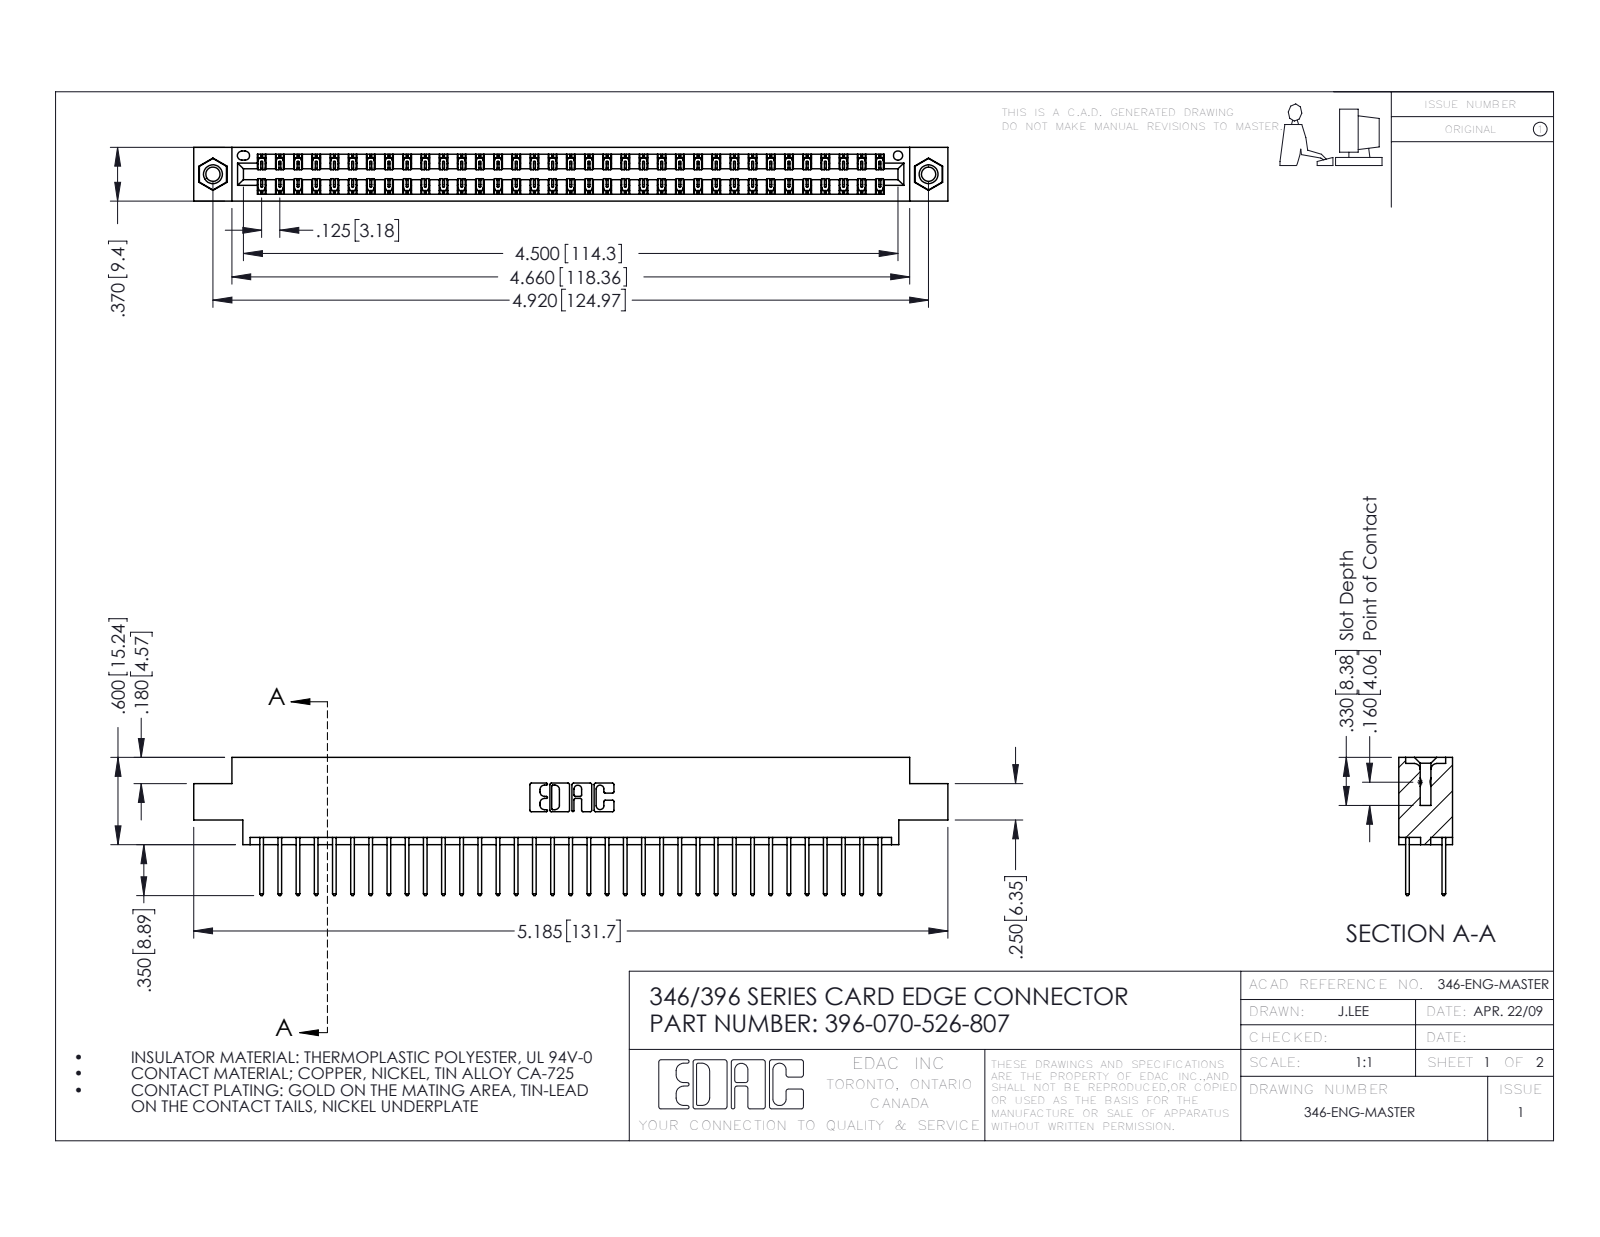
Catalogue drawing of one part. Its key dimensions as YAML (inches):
part_name: "345-292-001_345-293-126; 345-250-001_345-250-005-103; 346 Part_0.170 Offset - 0.156 Dia-TI; 396-070-526-807"
step_written_by: "SolidWorks 2016 (CONFIG_CONTROL_DESIGN)"
units: inches
bodies: {solids: 73, faces: 3826, planar: 2562, cylindrical: 1248, other: 16}
overall_size: [5.185, 0.95, 0.37]
volume: 0.777
surface_area: 28.09
round_holes:
  - {diameter: 0.098, count: 2}
  - {diameter: 0.125, count: 2}
  - {diameter: 0.156, count: 2}
  - {diameter: 0.064, count: 1}
round_bosses_or_shafts:
  - {diameter: 0.155, count: 2}
partial_cylinders:
  - {radius: 0.006, count: 105}
  - {radius: 0.01, count: 70}
  - {radius: 0.01, count: 22}
  - {radius: 0.007, count: 6}
  - {radius: 0.031, count: 6}
  - {radius: 0.026, count: 3}
  - {radius: 0.014, count: 2}
  - {radius: 0.022, count: 2}
face_to_face_distances: [0.048, 0.322, 0.25, 0.37, 0.072, 0.298, 0.025, 0.275, 0.222, 0.148]
hole_center_spacings: [0.246, 4.711, 4.92]
